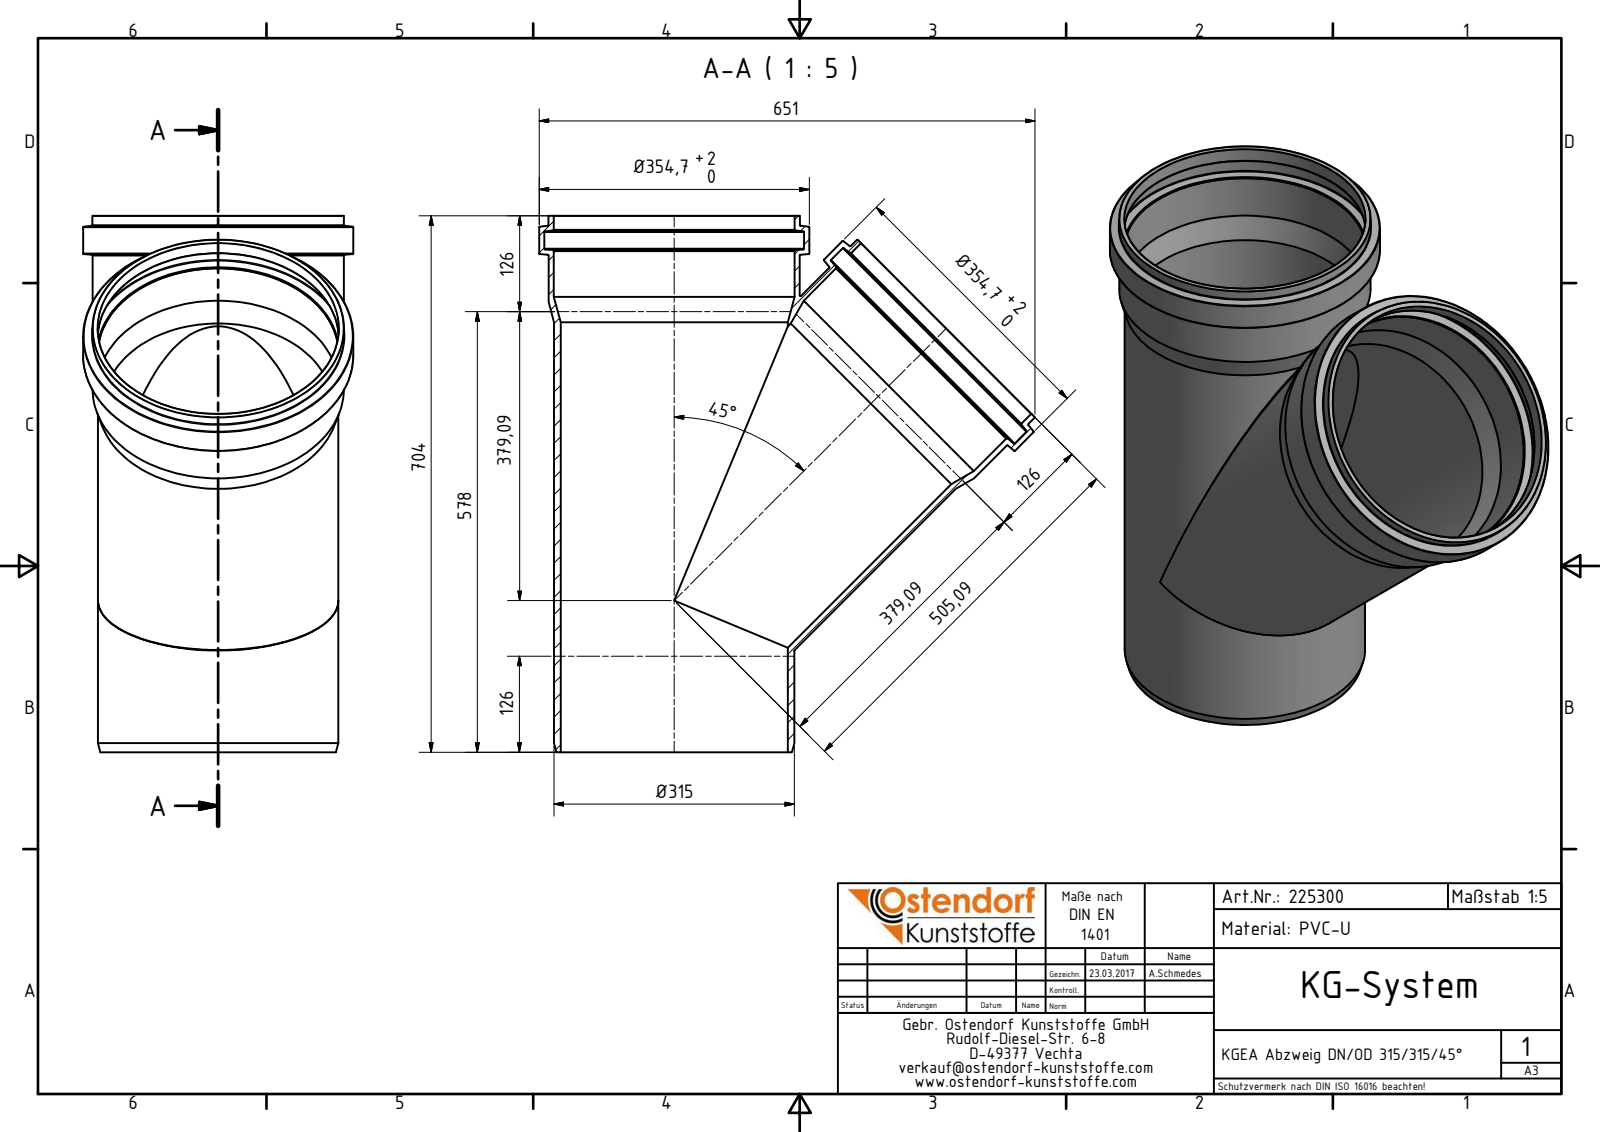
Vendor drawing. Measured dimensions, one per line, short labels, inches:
name: 225300 KGEA Abzweig DN_OD 315_315_45°
written by: Autodesk Inventor 2016 (AUTOMOTIVE_DESIGN)
unit: in
bodies: 1 solid, 62 faces (5 planar, 18 cylindrical, 39 other)
size: 27.717 × 25.63 × 13.965
volume: 479.7 in³; area: 3 009 in²
holes: 3× ⌀12.453, 2× ⌀11.74, 2× ⌀12.441, 2× ⌀13.421
bosses: 2× ⌀13.965, 2× ⌀12.996, 2× ⌀12.984, 2× ⌀12.425
face distances: 27.717, 25.883, 1.833, 1.832
